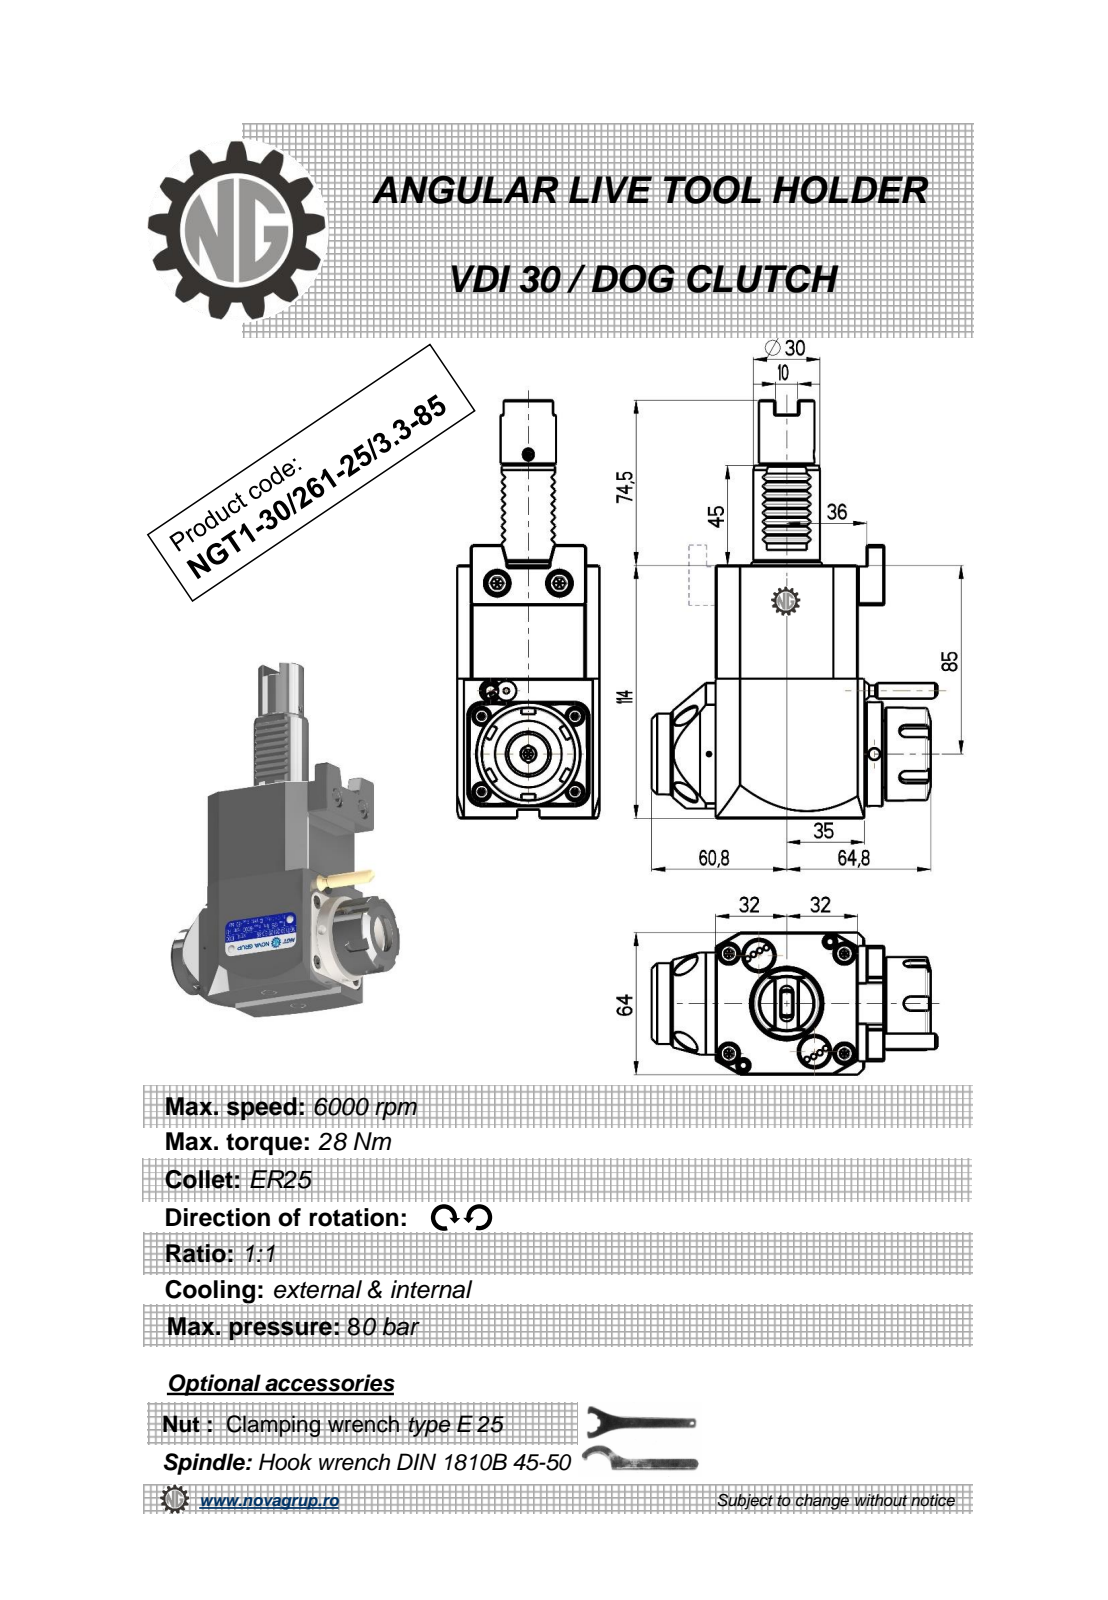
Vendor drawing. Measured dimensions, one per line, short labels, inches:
name: NGT1_30_261_25_3_3_85
written by: PRO/ENGINEER BY PARAMETRIC TECHNOLOGY CORPORATION, 2010280 (CONFIG_CONTROL_DESIGN)
unit: in
bodies: 1 solid, 428 faces (220 planar, 72 cylindrical, 136 other)
size: 7.421 × 5.064 × 2.52
volume: 36.98 in³; area: 89.6 in²
holes: 2× ⌀0.197, 1× ⌀0.098, 1× ⌀0.118, 1× ⌀0.165, 1× ⌀0.799
bosses: 1× ⌀1.85, 1× ⌀1.654, 1× ⌀1.437, 1× ⌀1.378, 1× ⌀1.181, 1× ⌀0.984, 1× ⌀0.353, 1× ⌀0.276
rounds: 16× R0.012, 6× R0.01, 5× R0.118, 2× R0.02, 2× R0.039, 2× R6.299, 1× R1.26
face distances: 2.52, 4.488, 0.354, 0.02, 0.118, 3.78, 2.646, 0.126, 3.009, 2.638
hole spacings: 1.307, 4.246, 5.315
